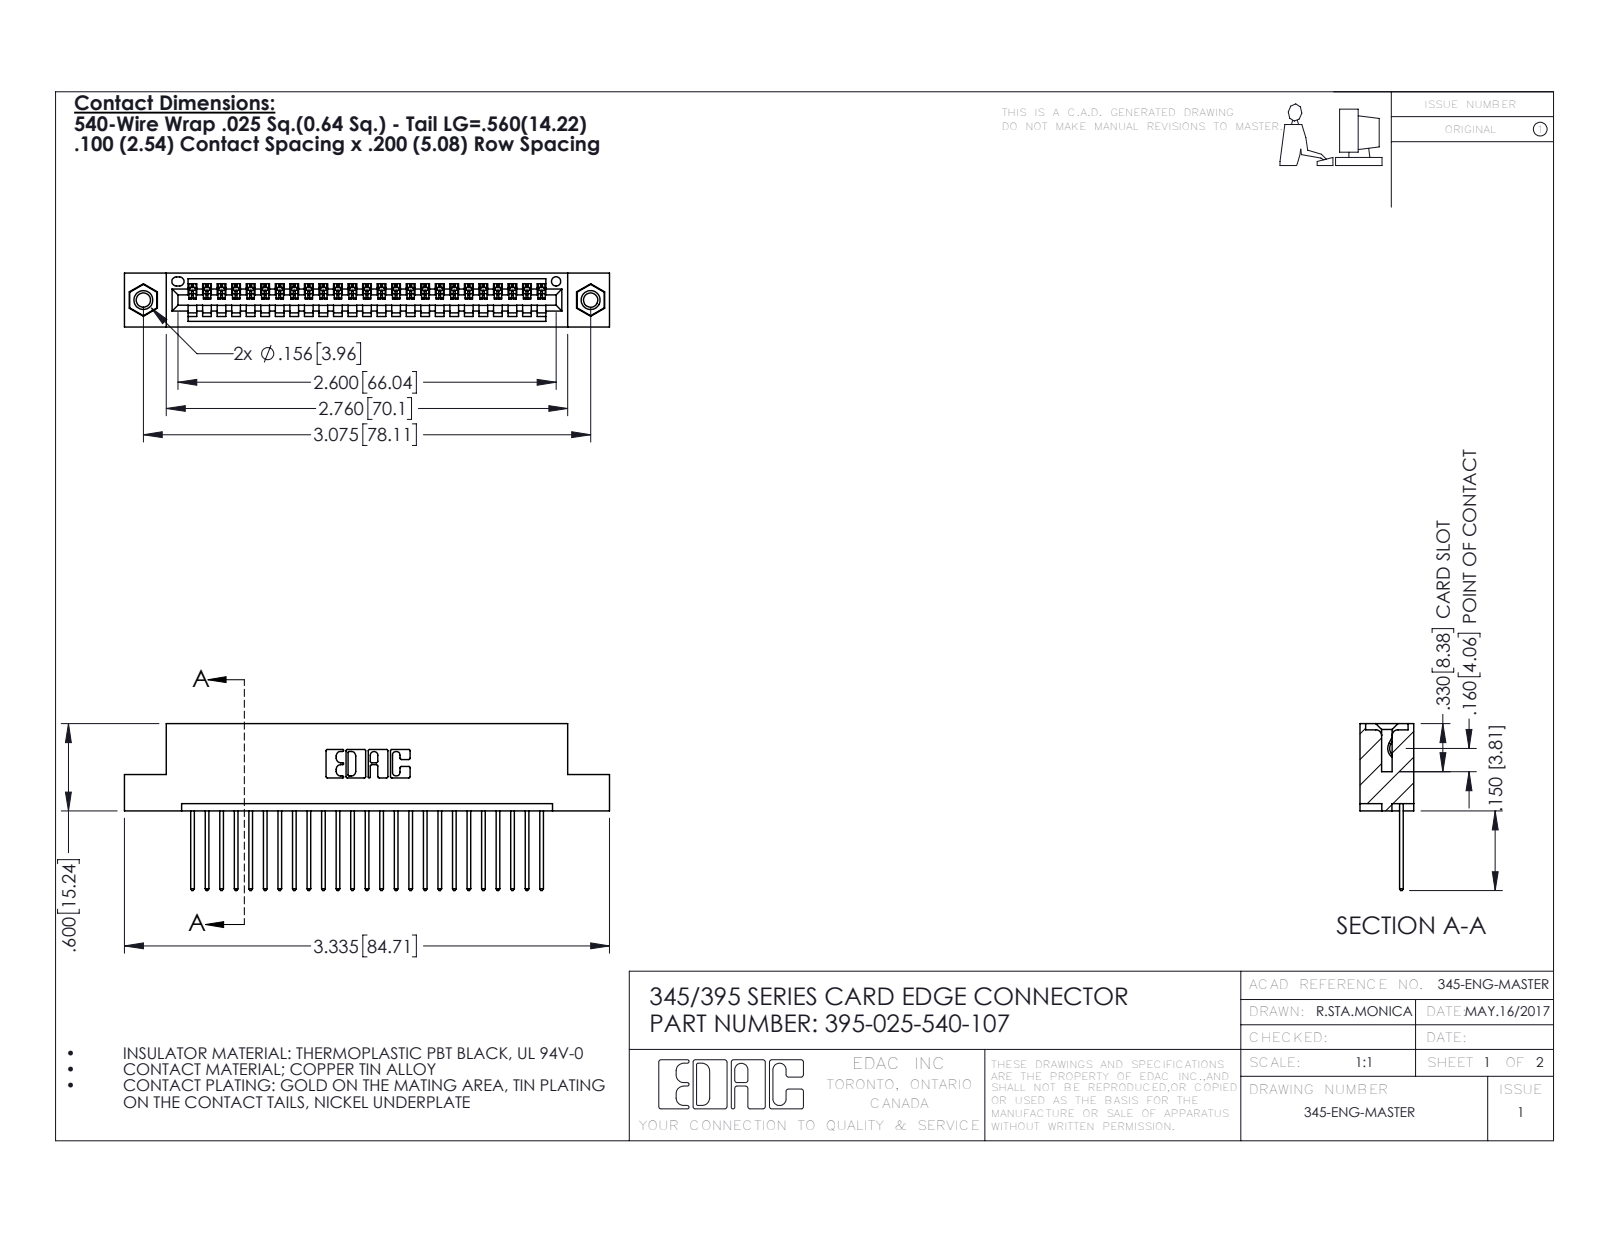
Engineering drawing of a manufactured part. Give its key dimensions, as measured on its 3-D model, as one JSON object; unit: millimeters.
{"part_name": "345-292-001_345-293-140; 345 Part_Flush Mounting Lugs - 0.156 Dia-TI; 395-025-540-107; 345-250-001_345-250-005-103", "step_written_by": "SolidWorks 2016 (CONFIG_CONTROL_DESIGN)", "units": "millimeters", "bodies": {"solids": 28, "faces": 1636, "planar": 1112, "cylindrical": 508, "other": 16}, "overall_size": [84.7, 29.1, 9.4], "volume_mm3": 7930, "surface_area_mm2": 10580, "round_holes": [[2.5, 2], [3.2, 2], [4, 2], [1.6, 1]], "round_bosses_or_shafts": [[3.9, 2]], "partial_cylinders_radius": [[0.2, 50], [0.3, 50], [0.3, 22], [0.2, 6], [0.8, 6], [0.7, 3], [0.8, 2], [1, 2]], "face_to_face_distances": [1.8, 7.6, 5.1, 9.4, 2.5, 6.9, 0.6, 5.7, 3.8, 1.8], "hole_center_spacings": [6.9, 72.1, 78.1]}
